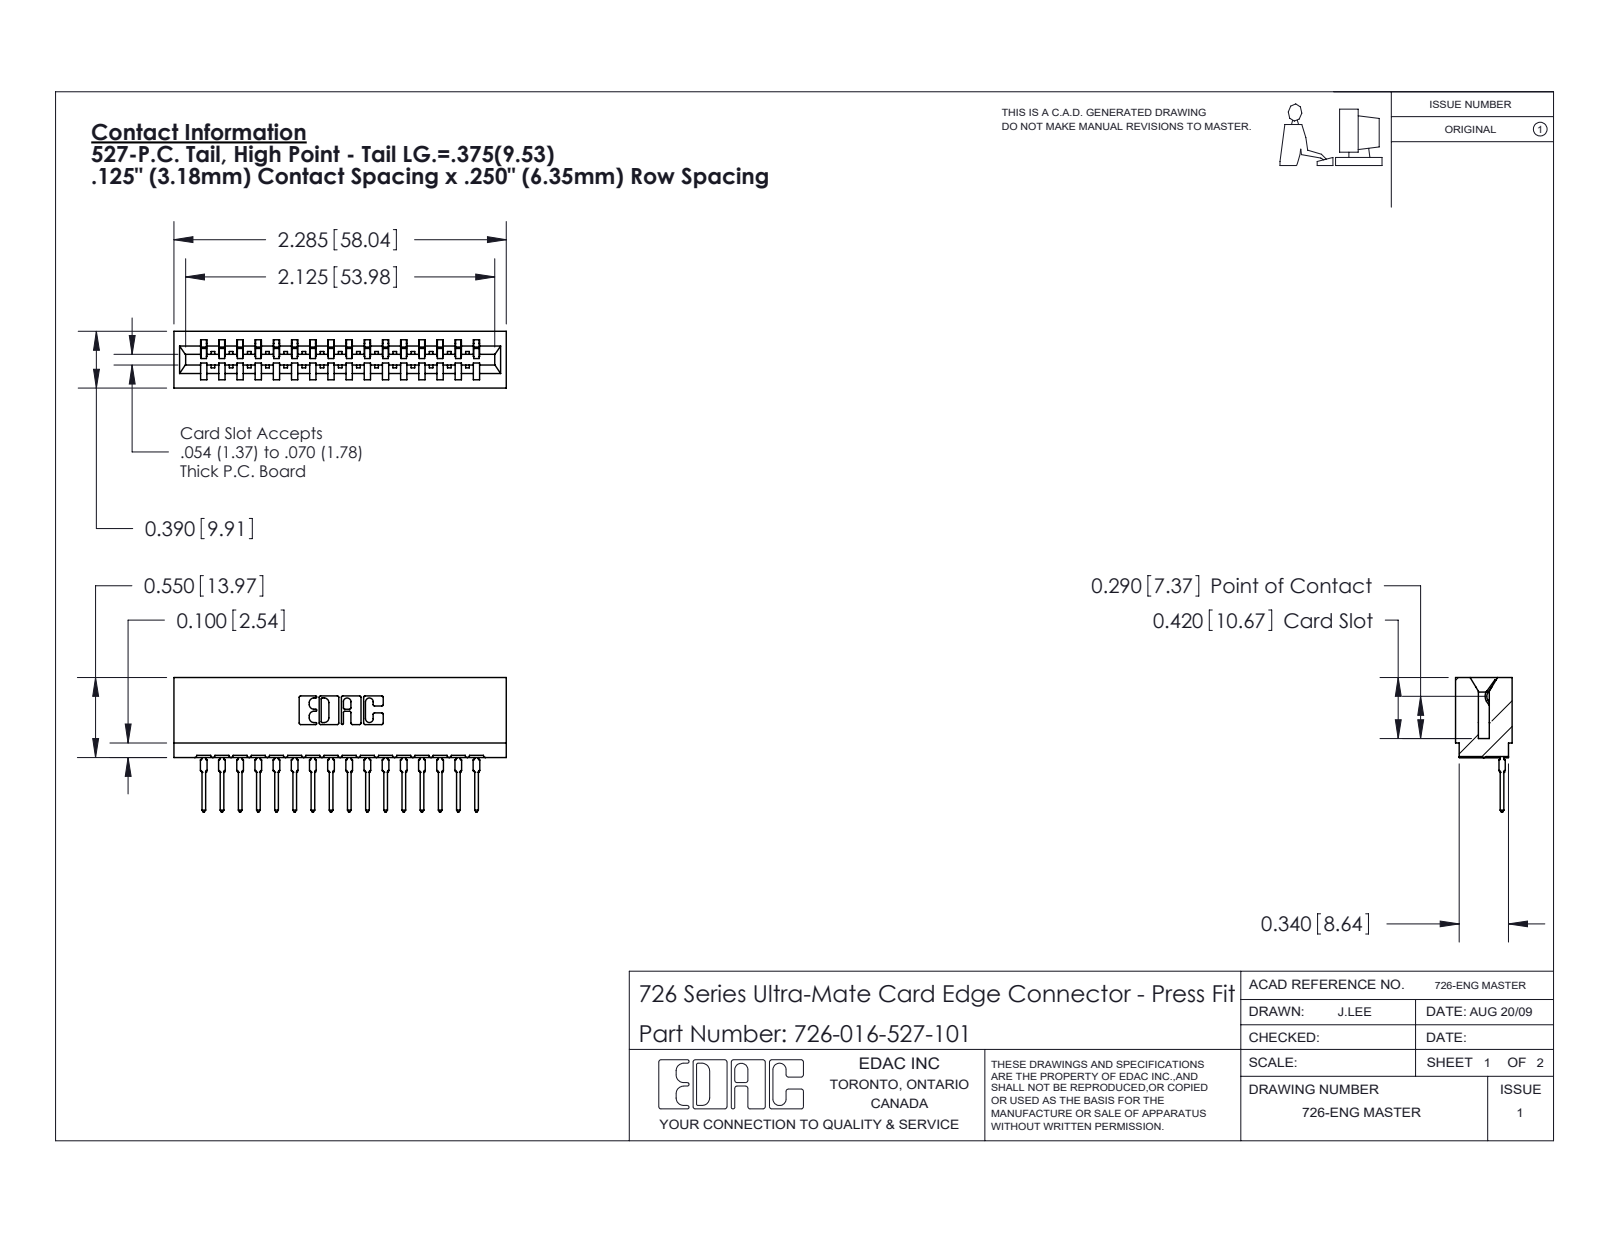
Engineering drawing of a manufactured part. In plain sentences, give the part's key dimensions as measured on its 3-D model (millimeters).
The part is named "746-292-001_527; 726 Part_.515 Slot Depth - 01; 726-016-527-101". Its 3-D file was written by "SolidWorks 2020 (CONFIG_CONTROL_DESIGN)". It is 17 solids with 1825 faces: 1063 planar, 346 cylindrical and 416 other. Overall it measures 58 by 23.5 by 9.9 millimeters. Its volume is 5 340 cubic millimeters and its surface area 7 871 square millimeters. Partial cylindrical surfaces (rounded edges, fillets, slot ends): 32 of radius 0.5, 22 of radius 0.3, 17 of radius 0.4, 6 of radius 0.2, 6 of radius 0.8, 4 of radius 0.1, 4 of radius 0.3, 3 of radius 0.7. The main face-to-face distances are 1.4, 8.5, 6.4, 12.7, 9.9, 0.6, 7.8, 3.2, 19.1, 9.5.
